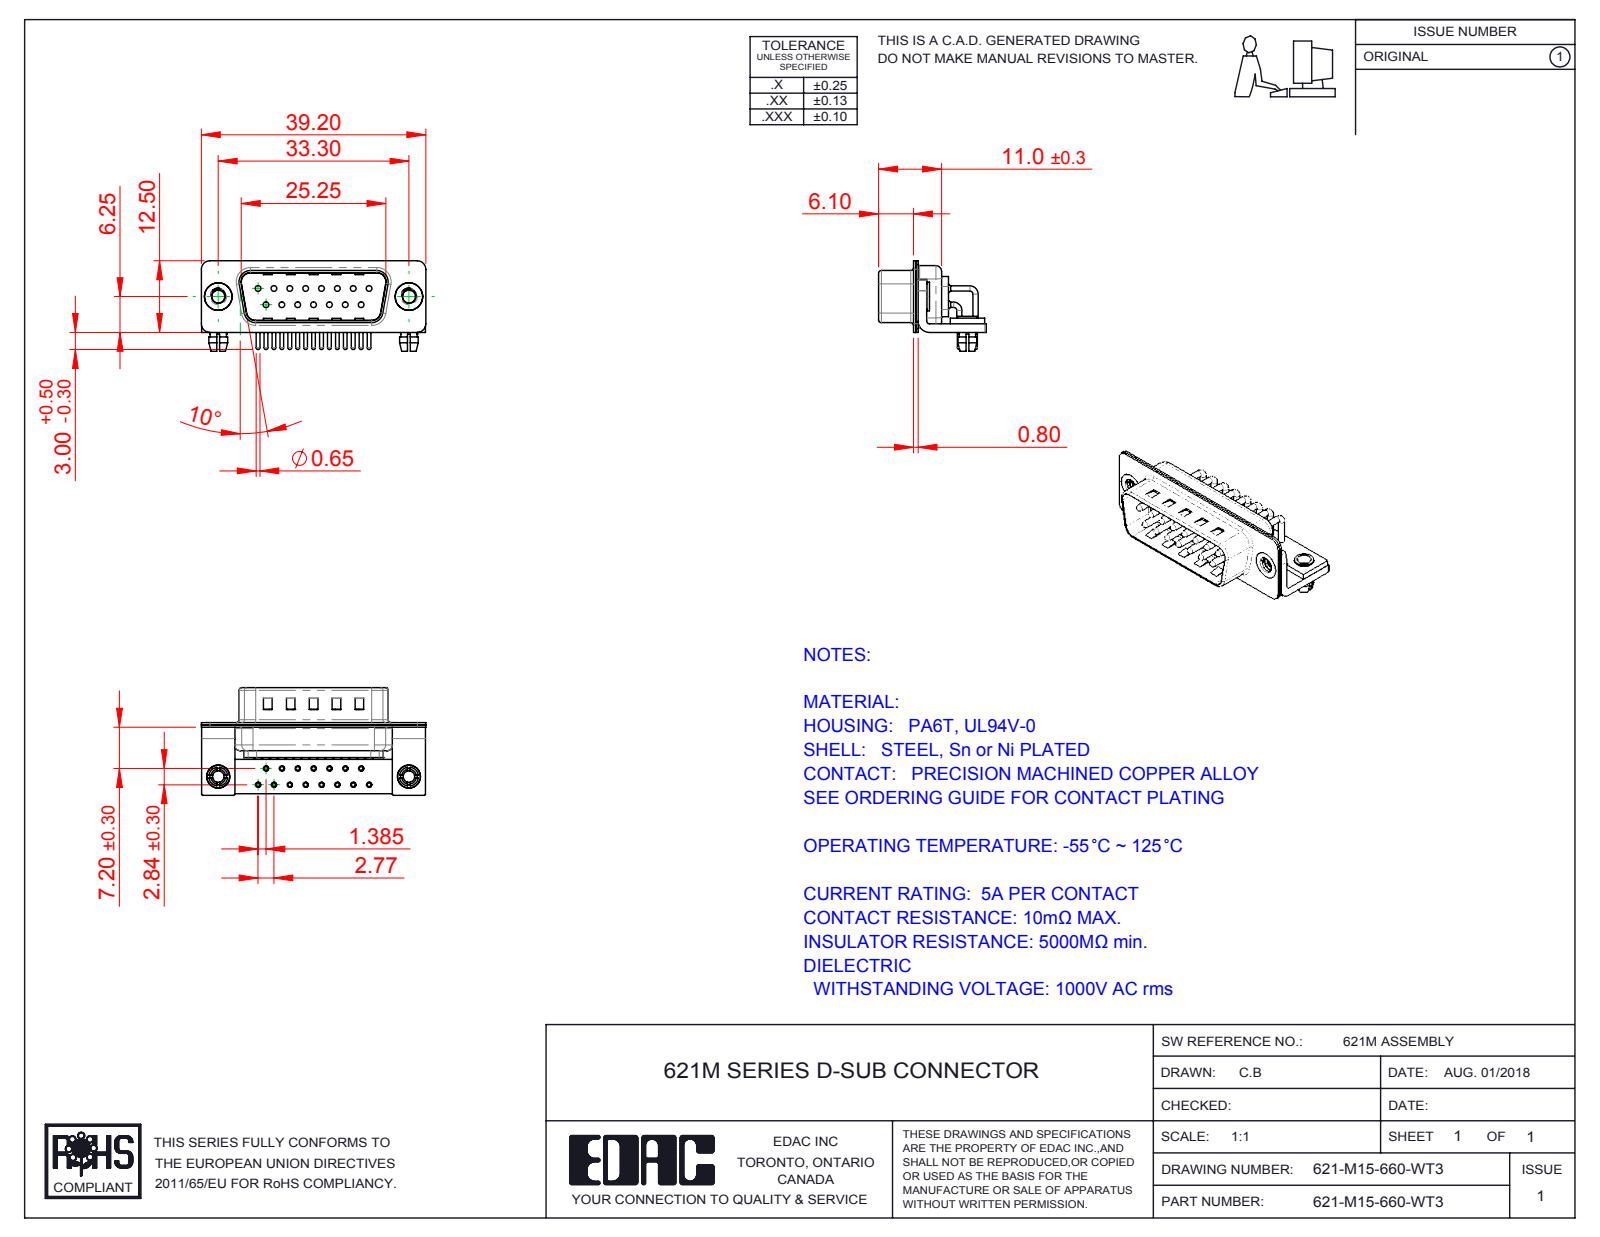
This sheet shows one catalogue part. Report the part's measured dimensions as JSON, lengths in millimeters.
{"part_name": "621M 4-40 Threaded Rivet_Stabilizer; 621M Housing_15 Contacts; 621M Shell Rear_15 Contacts; 621M Shell Front_15 Contacts (+6 more)", "step_written_by": "SolidWorks 2016 (CONFIG_CONTROL_DESIGN)", "units": "millimeters", "bodies": {"solids": 25, "faces": 2162, "planar": 1173, "cylindrical": 757, "other": 232}, "overall_size": [39.2, 18.8, 15.8], "volume_mm3": 2417, "surface_area_mm2": 6593, "round_holes": [[2, 17], [0.9, 15], [1, 15], [1.7, 15], [2.26, 2], [2.5, 2], [3.2, 2], [4, 2], [4.8, 2]], "round_bosses_or_shafts": [[0.9, 22], [1.5, 15], [0.65, 15], [5, 2], [4.9, 2], [4, 2], [3.4, 2], [3.3, 2]], "partial_cylinders_radius": [[0.25, 16], [1.5, 16], [1.01, 15], [2, 13], [0.5, 9], [1.6, 8], [0.6, 4], [0.65, 4]], "face_to_face_distances": [0.4, 0.85, 1.5, 0.8, 1.25, 10.4, 9.55, 1, 2.1, 1.9], "hole_center_spacings": [3.16, 2.77, 5.54, 8.31, 11.08, 5.03, 5.04, 7.48]}
